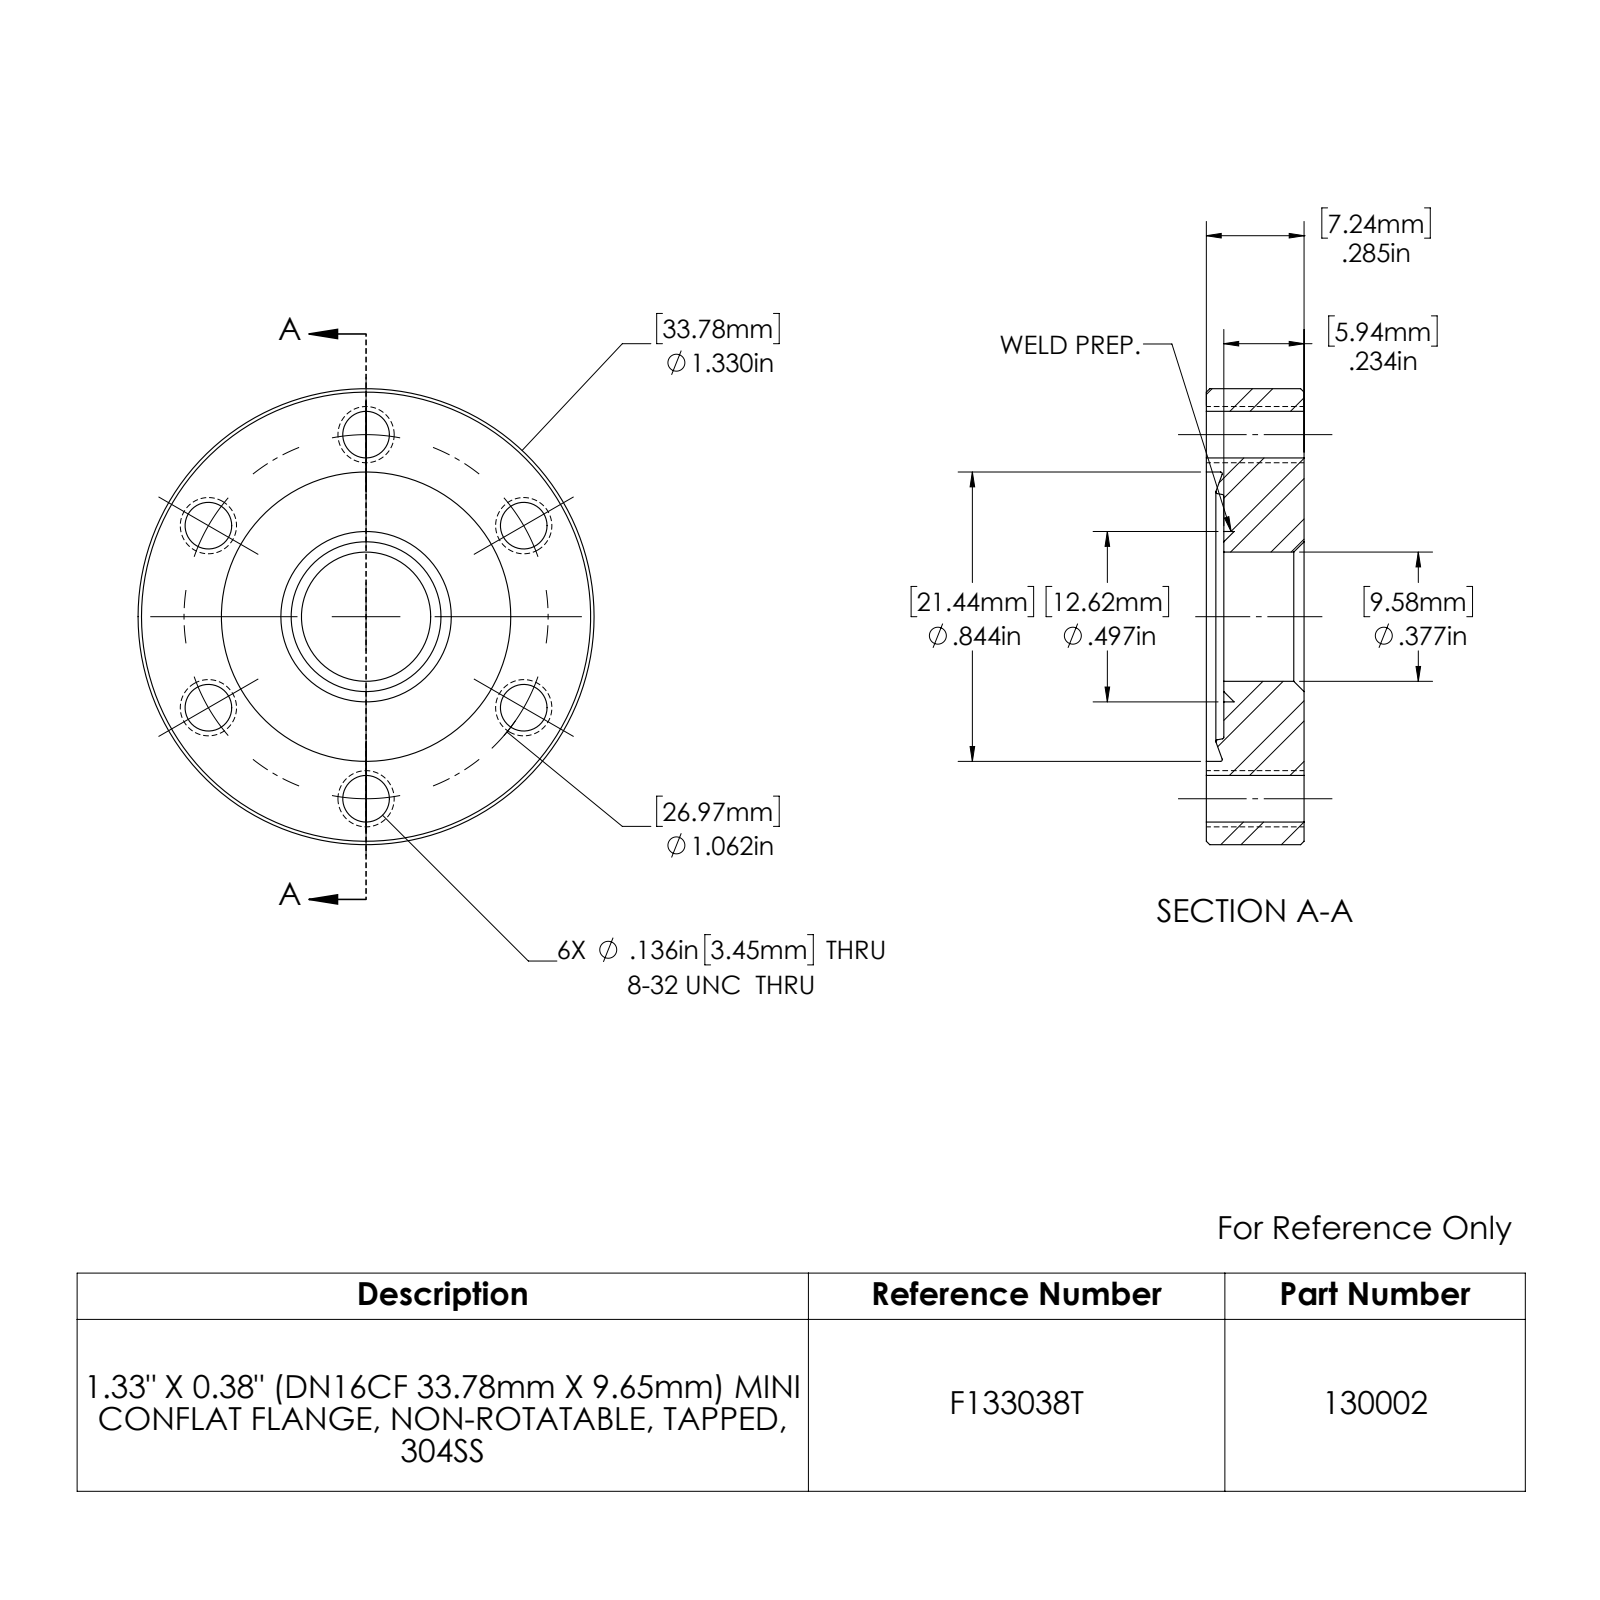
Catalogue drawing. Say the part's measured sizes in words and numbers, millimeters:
The part is named "130002". Its 3-D file was written by "SolidWorks 2022 (AUTOMOTIVE_DESIGN)". It is 1 solid with 42 faces: 4 planar, 20 cylindrical and 18 other. Overall it measures 33.8 by 33.8 by 7.2 millimeters. Its volume is 5 190 cubic millimeters and its surface area 3 057 square millimeters. Round holes: 6 of diameter 3.5, 1 of diameter 9.6, 1 of diameter 12.6, 1 of diameter 21.4. Round bosses or shafts: 1 of diameter 33.8. The main face-to-face distances are 7.2, 1.3, 5.9. The hole center spacings are 13.5, 23.4, 13.5, 27, 27.
